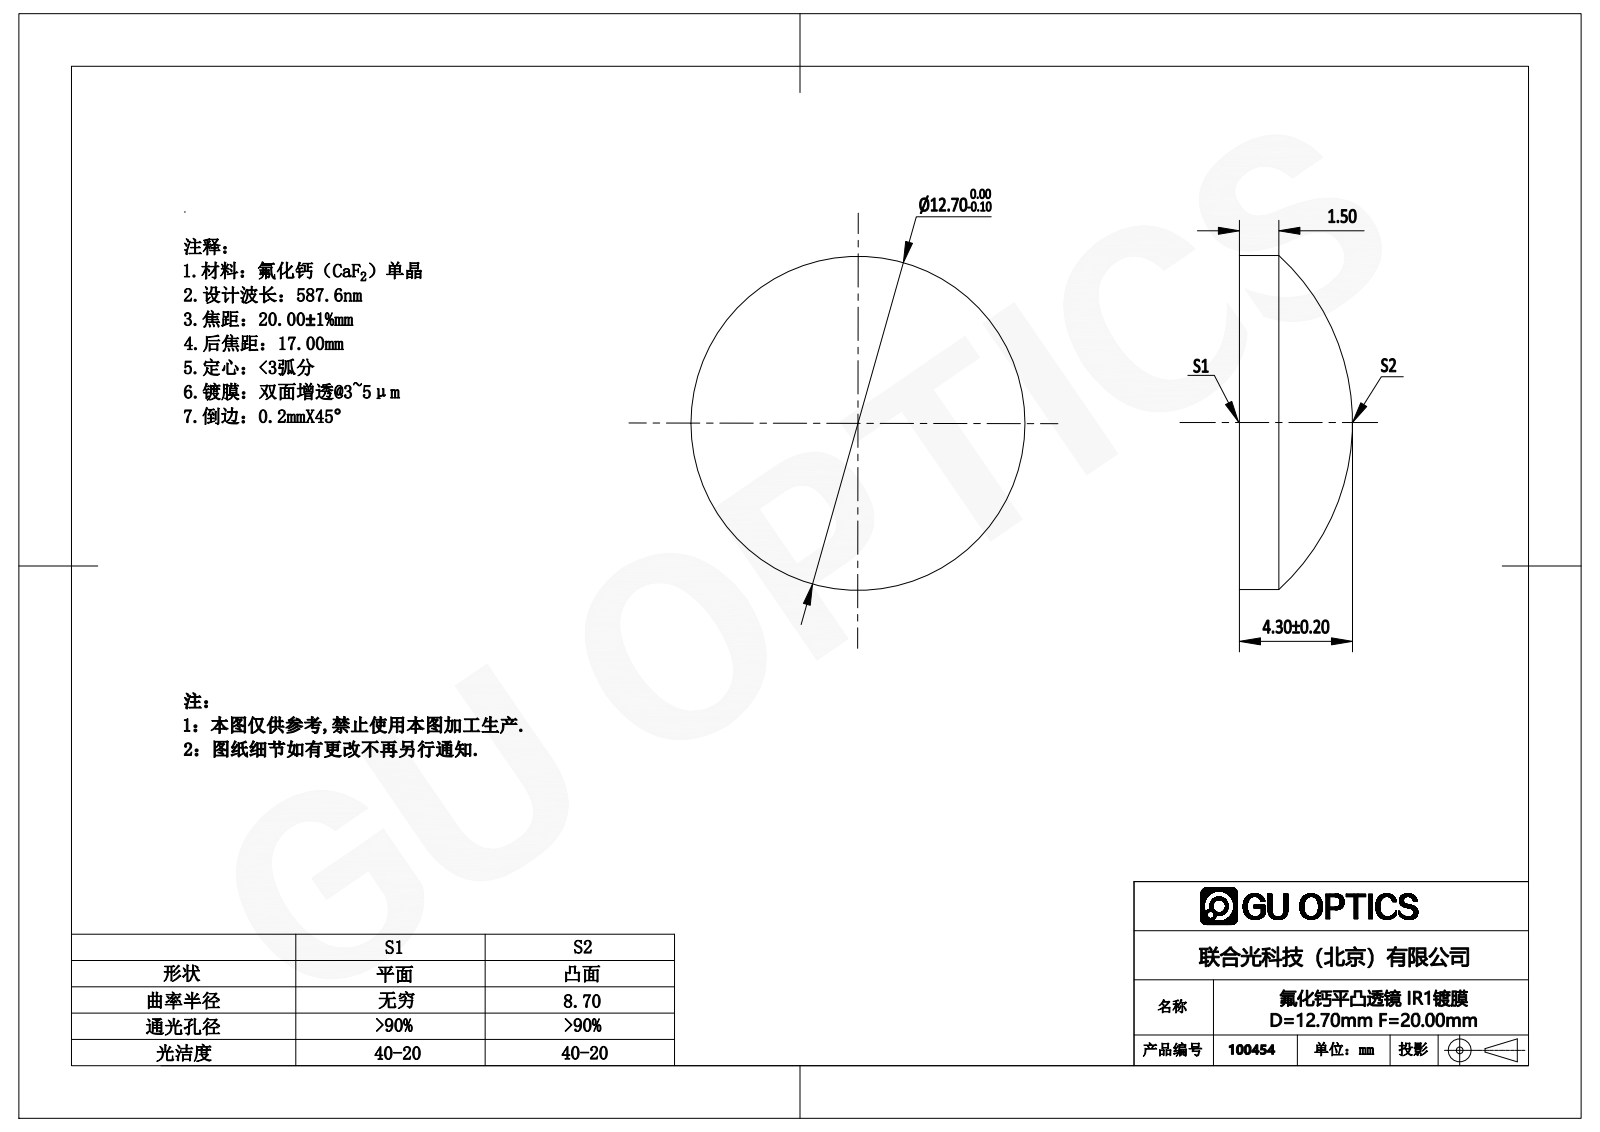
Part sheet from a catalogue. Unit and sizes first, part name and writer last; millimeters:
Units: millimetres
Overall size (bounding box): 12.7 × 12.7 × 4.3
Round bosses / shafts (diameter × count): ⌀12.7 ×1
Volume: 379 mm³ · Surface area: 338 mm²
Bodies: 1 solid, 5 faces (1 planar, 2 cylindrical, 2 other)
Part name (STEP PRODUCT): 100444
STEP written by: SolidWorks 2016 (AUTOMOTIVE_DESIGN)
